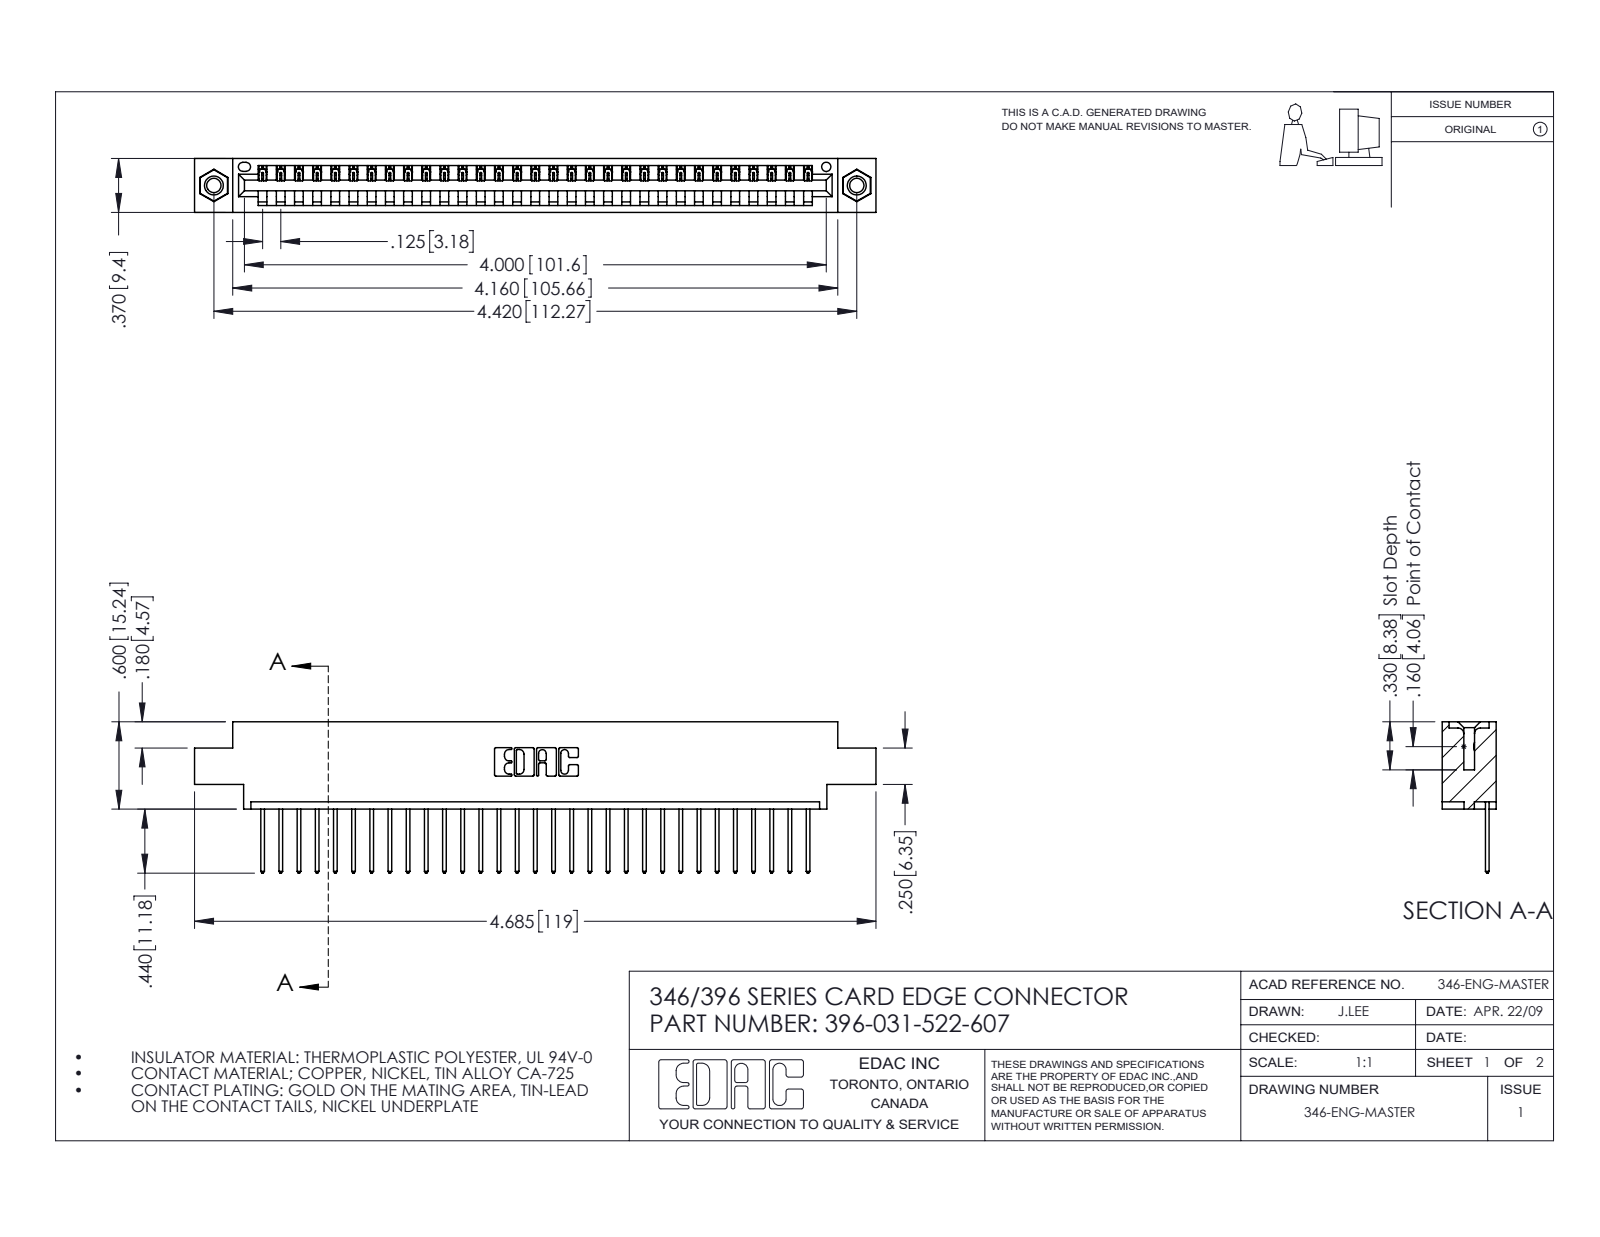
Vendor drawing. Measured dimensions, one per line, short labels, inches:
name: 346 Part_0.170 Offset - 0.156 Dia-TI; 396-031-522-607; 345-250-001_345-250-005-103; 345-292-001_345-293-122
written by: SolidWorks 2016 (CONFIG_CONTROL_DESIGN)
unit: in
bodies: 34 solids, 1984 faces (1352 planar, 616 cylindrical, 16 other)
size: 4.685 × 1.04 × 0.37
volume: 0.68 in³; area: 21.9 in²
holes: 2× ⌀0.098, 2× ⌀0.125, 2× ⌀0.156, 1× ⌀0.064
bosses: 2× ⌀0.155
rounds: 62× R0.006, 62× R0.01, 22× R0.01, 6× R0.007, 6× R0.031, 3× R0.026, 2× R0.031, 2× R0.04
face distances: 0.048, 0.322, 0.37, 0.25, 0.072, 0.298, 0.025, 0.222, 0.148, 0.1
hole spacings: 0.246, 4.212, 4.42
